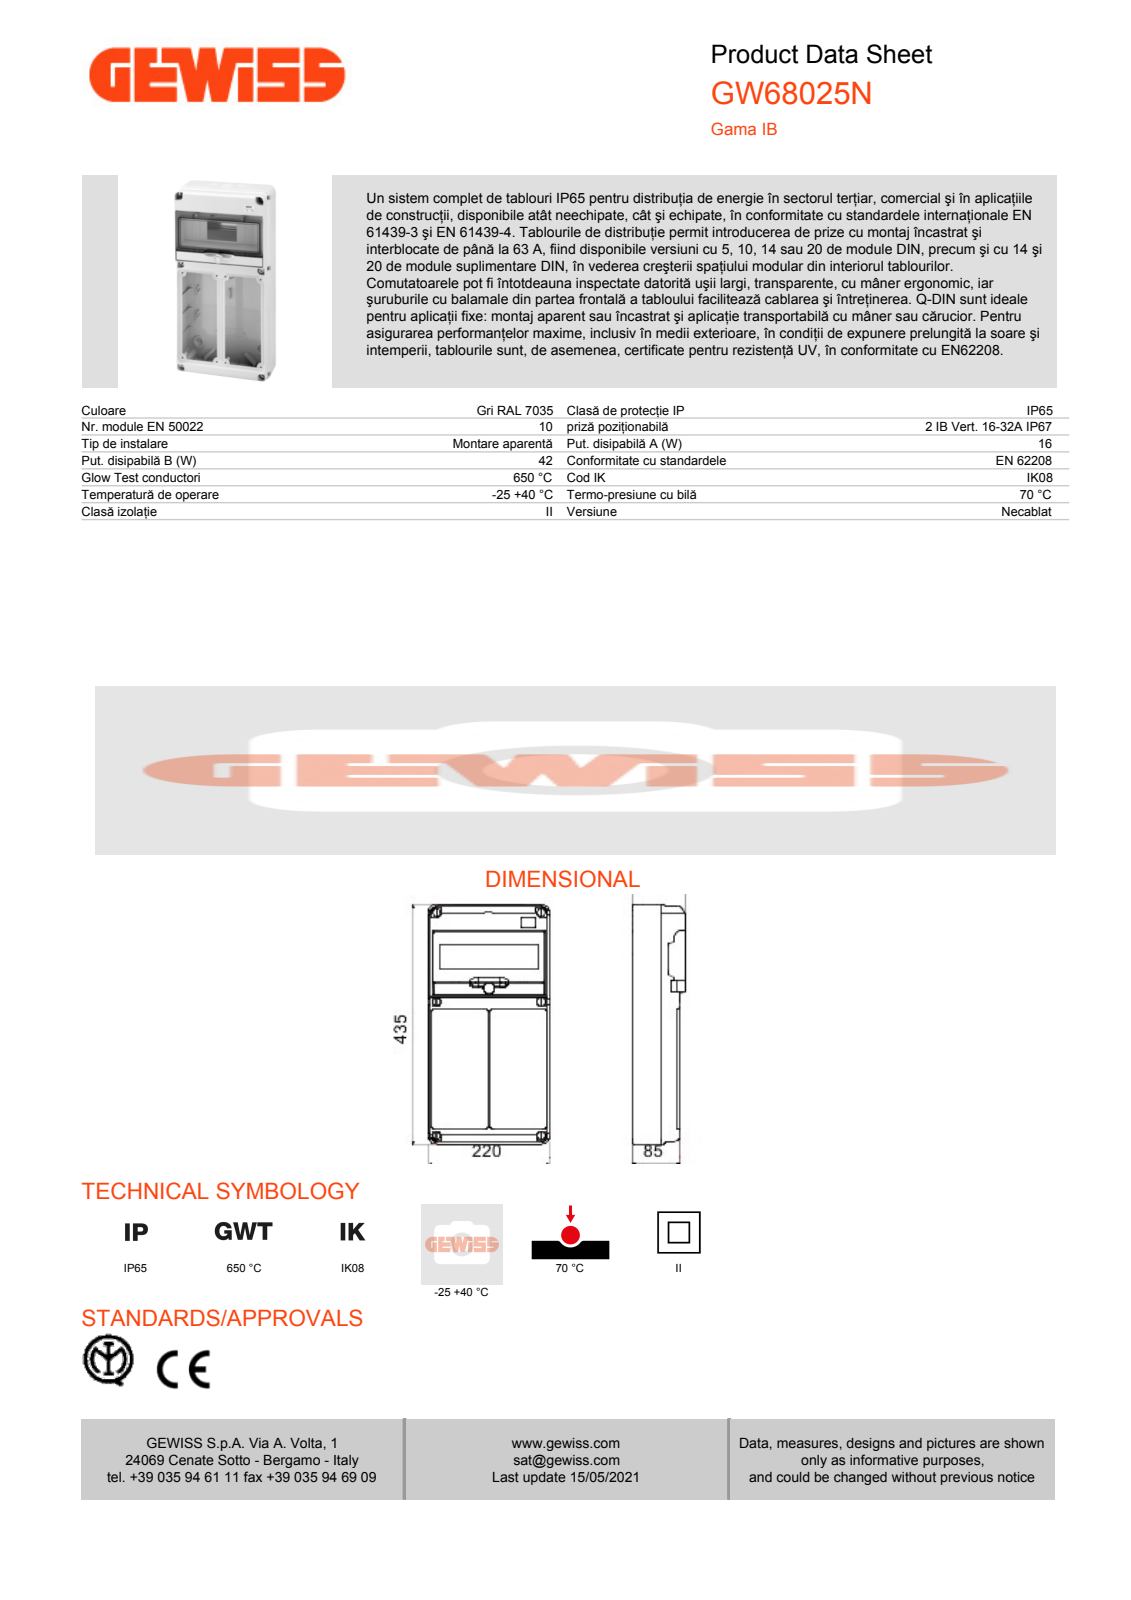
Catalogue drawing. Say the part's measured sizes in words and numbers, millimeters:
The part is named "55525067E_FRONTALE_QDIN_10M_2PR; 55525059_FONDO_QDIN_10M; GW68025N_ASM". Its 3-D file was written by "CREO PARAMETRIC BY PTC INC, 2020074 (CONFIG_CONTROL_DESIGN)". It is 2 solids with 1187 faces: 584 planar, 227 cylindrical and 376 other. Overall it measures 435 by 220 by 102.72 millimeters. Its volume is 1 698 000 cubic millimeters and its surface area 622 406 square millimeters. Partial cylindrical surfaces (rounded edges, fillets, slot ends): 50 of radius 2, 27 of radius 1.7, 16 of radius 1, 15 of radius 0.5, 10 of radius 9, 8 of radius 4.25, 8 of radius 6.5, 8 of radius 6.7. The main face-to-face distances are 3, 95, 92, 2.2, 2.97, 212.69, 220, 30.8, 12, 209.72.
